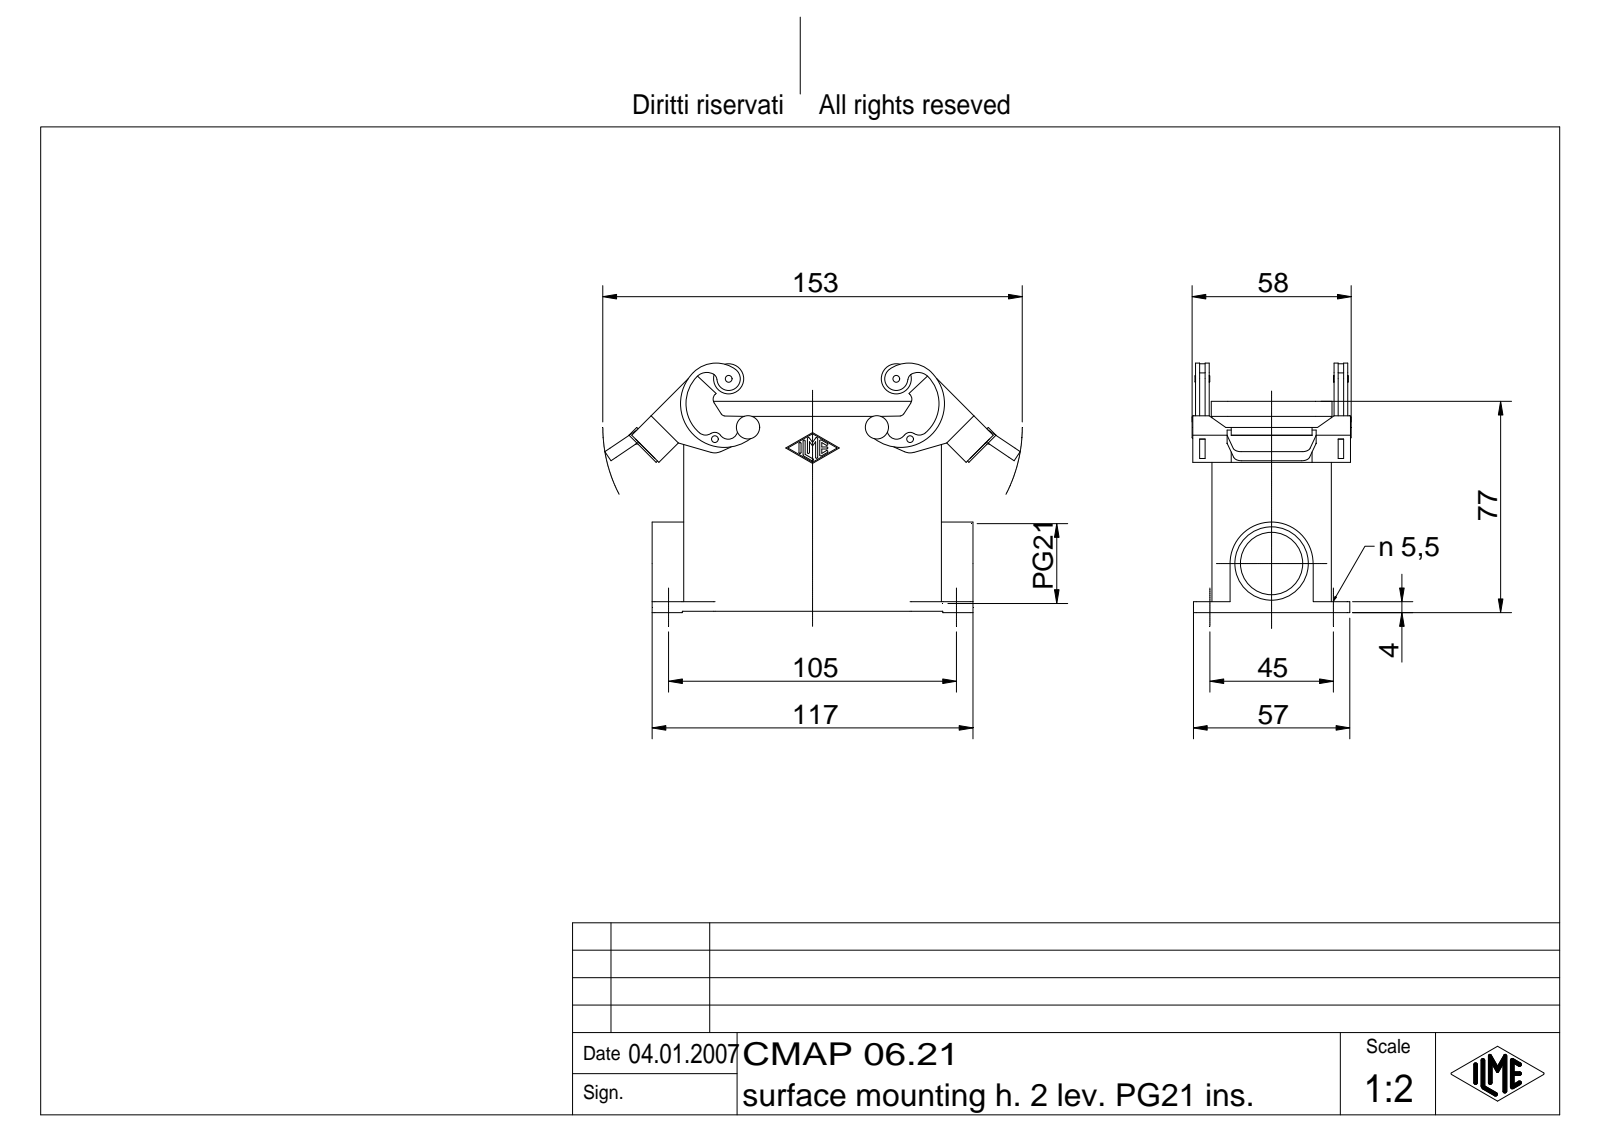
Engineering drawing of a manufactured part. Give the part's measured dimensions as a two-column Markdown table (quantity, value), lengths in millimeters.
| quantity | value |
| --- | --- |
| part name | CMAP 06.21 |
| STEP written by | Autodesk Inventor 7 (AUTOMOTIVE_DESIGN) |
| units | millimeters |
| bodies | 1 solid, 717 faces (191 planar, 185 cylindrical, 341 other) |
| overall size | 151.49 × 90.94 × 58 |
| volume | 125 810 mm³ |
| surface area | 68 987 mm² |
| round holes (diameter × count) | 2 × 4, 5.5 × 4, 2.5 × 2, 22.78 × 1, 26.78 × 1 |
| round bosses / shafts (diameter × count) | 11 × 2, 5 × 2, 3 × 2 |
| partial cylindrical surfaces (radius × count) | 0.38 × 14, 1 × 14, 3 × 8, 6 × 8, 2.5 × 6, 1.5 × 4, 2 × 4, 3.5 × 4 |
| main face-to-face distances | 3, 40.5, 43.5, 37.5, 3.5, 4, 0.75, 50.5, 11, 40.75 |
| hole center spacings | 22.56, 45, 71.62, 105, 114.24, 63.14, 73.18 |
